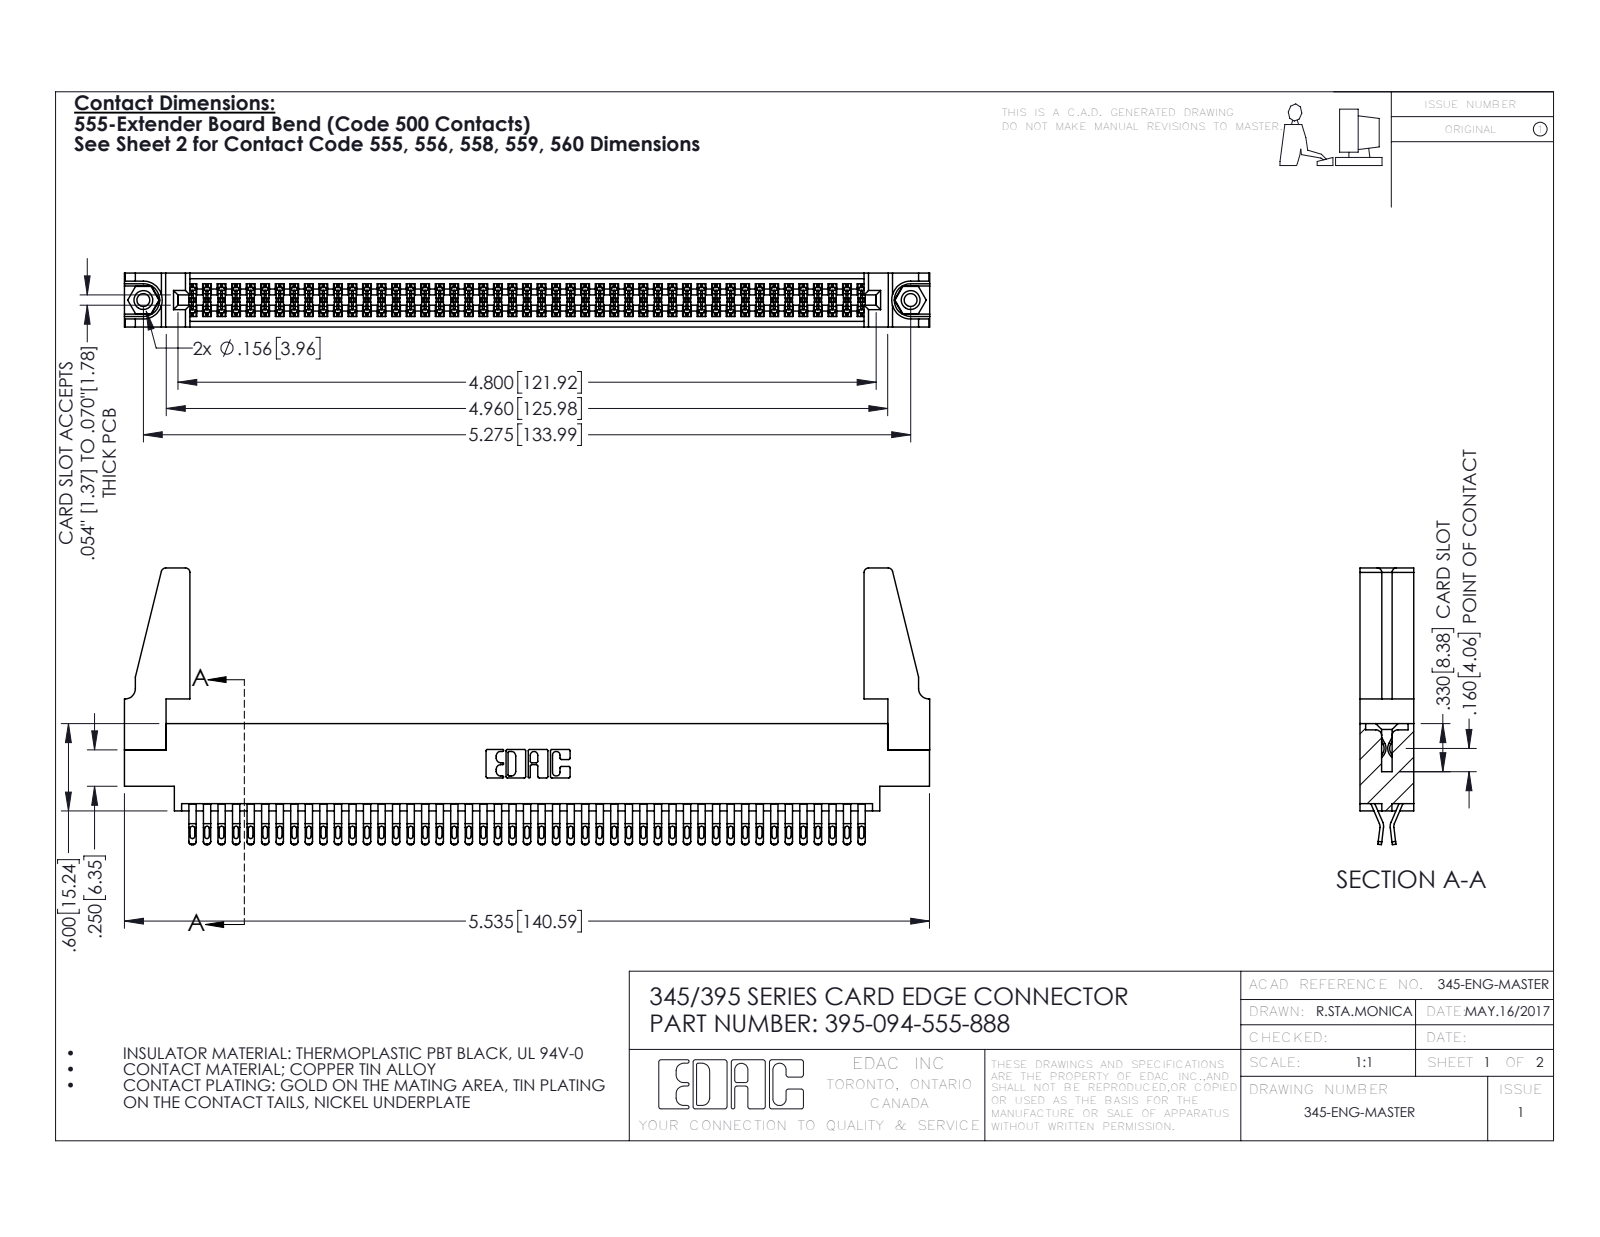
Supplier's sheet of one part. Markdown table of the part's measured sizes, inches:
| quantity | value |
| --- | --- |
| part name | 345-220-078_345-220-088; 345-292-001_555 Tail; 345-250-001_345-250-001-102; 345 Part_0.170 Offset - 0.156 Dia-TH (+1 more) |
| STEP written by | SolidWorks 2016 (CONFIG_CONTROL_DESIGN) |
| units | inches |
| bodies | 99 solids, 5518 faces (3070 planar, 2432 cylindrical, 16 other) |
| overall size | 5.536 × 1.902 × 0.37 |
| volume | 1.045 in³ |
| surface area | 38.45 in² |
| round holes (diameter × count) | 0.089 × 2, 0.125 × 2, 0.156 × 2, 0.064 × 1 |
| round bosses / shafts (diameter × count) | 0.155 × 2 |
| partial cylindrical surfaces (radius × count) | 0.016 × 235, 0.02 × 188, 0.006 × 141, 0.01 × 22, 0.03 × 8, 0.007 × 6, 0.031 × 6, 0.026 × 3 |
| main face-to-face distances | 0.072, 0.298, 0.37, 0.025, 0.098, 0.272, 0.2, 0.225, 0.175, 0.149 |
| hole center spacings | 0.27, 5.039, 5.275 |
